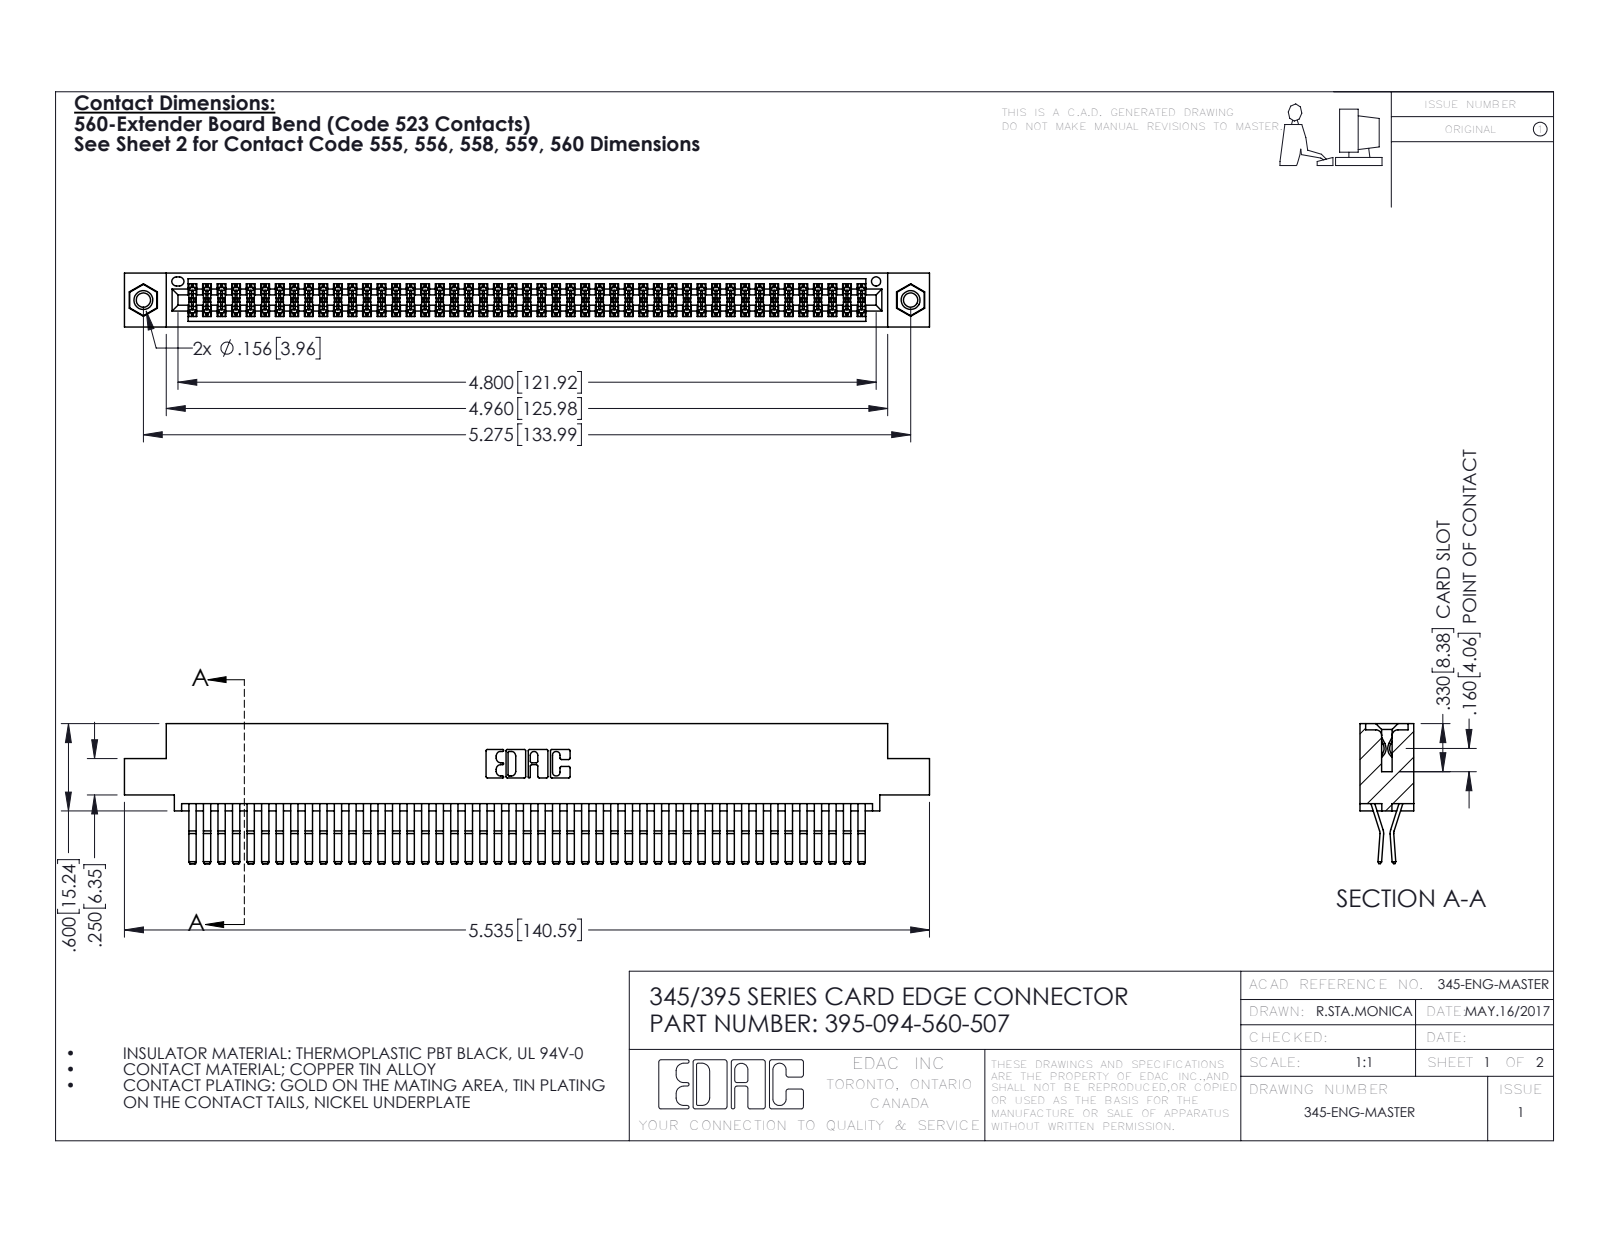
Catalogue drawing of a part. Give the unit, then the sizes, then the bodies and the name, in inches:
Units: inches
Overall size (bounding box): 5.535 × 0.962 × 0.37
Round holes (diameter × count): ⌀0.098 ×2, ⌀0.125 ×2, ⌀0.156 ×2, ⌀0.064 ×1
Round bosses / shafts (diameter × count): ⌀0.155 ×2
Partial cylindrical surfaces — rounded edges, fillets, slot ends (radius × count): R0.006 ×141, R0.01 ×22, R0.007 ×6, R0.031 ×6, R0.026 ×3, R0.01 ×2, R0.014 ×2, R0.019 ×2
Main face-to-face distances: 0.025, 0.072, 0.298, 0.37, 0.2, 0.098, 0.272, 0.225, 0.175, 0.149
Hole centre spacings: 0.27, 5.039, 5.275
Volume: 0.869 in³ · Surface area: 35.4 in²
Bodies: 97 solids, 5078 faces (3218 planar, 1844 cylindrical, 16 other)
Part name (STEP PRODUCT): 345-250-001_345-250-005-103; 345 Part_0.110 Offset - 0.156 Dia-TI; 345-292-001_560 Tail; 395-094-560-507
STEP written by: SolidWorks 2016 (CONFIG_CONTROL_DESIGN)
